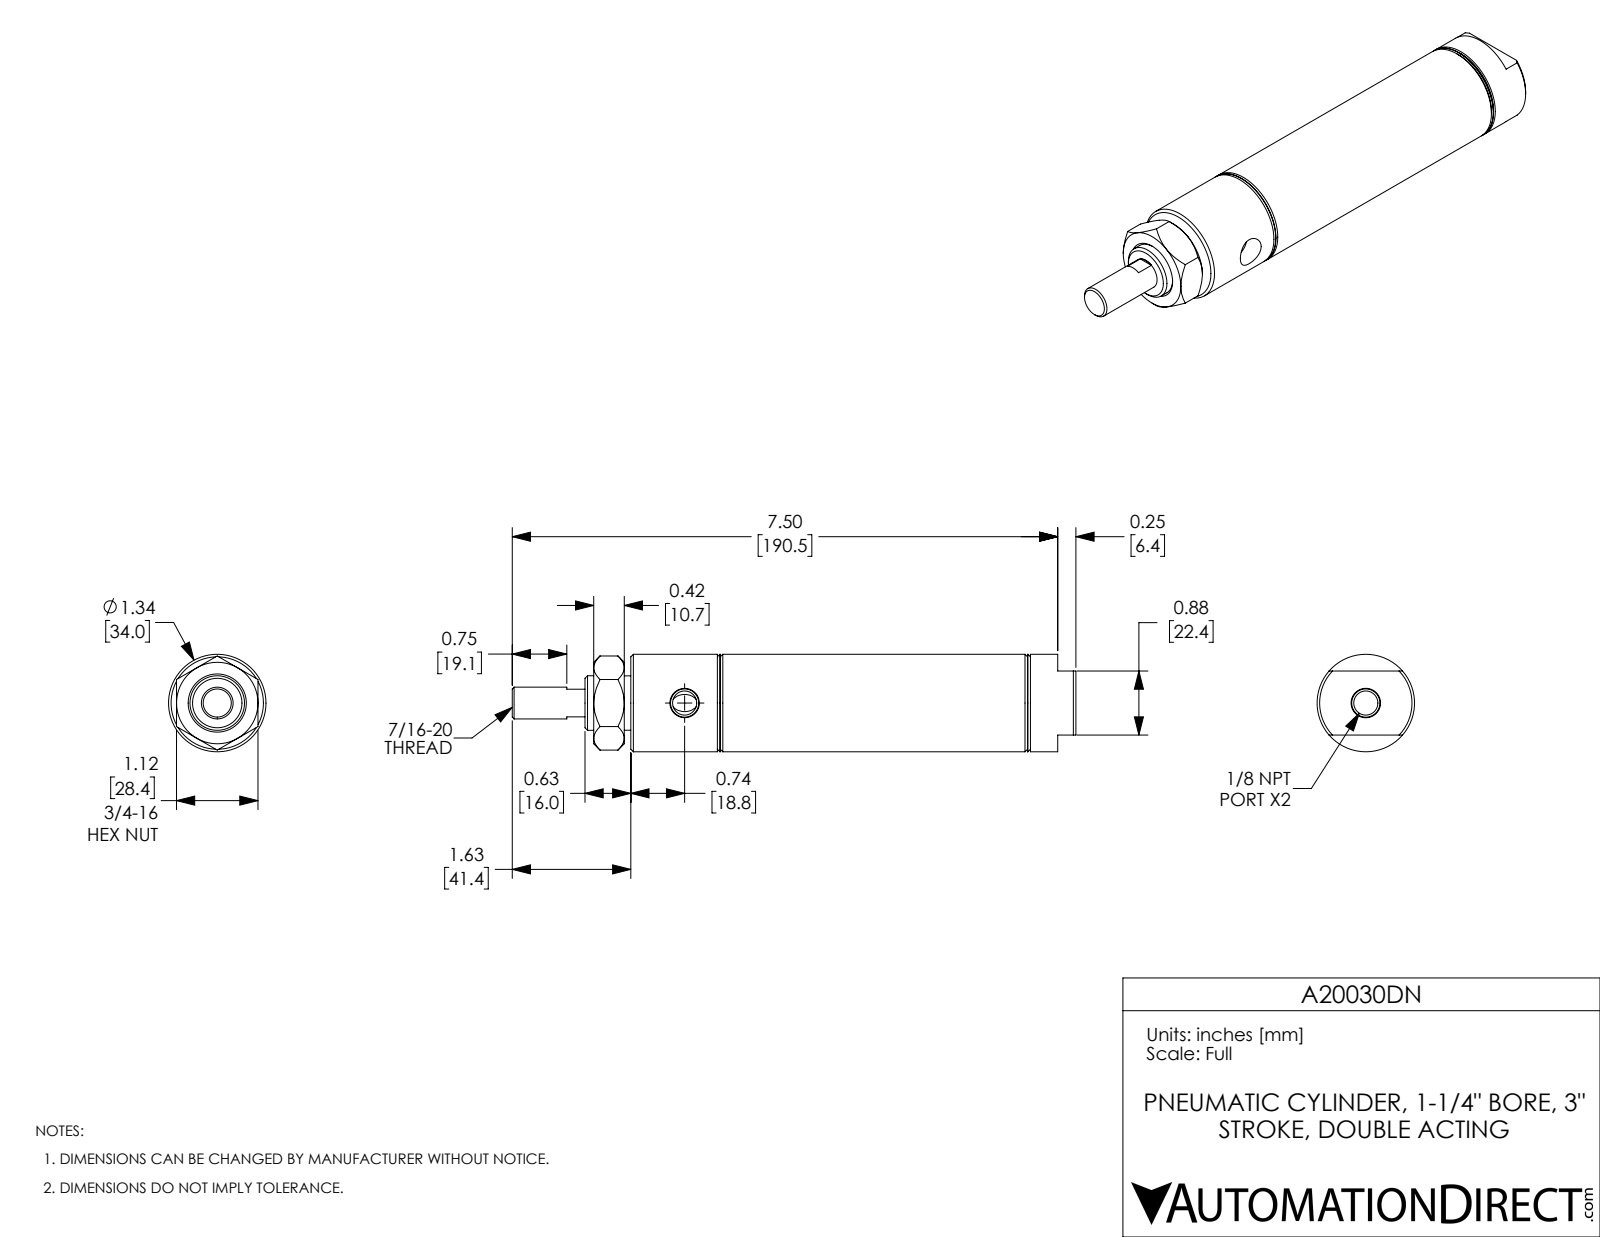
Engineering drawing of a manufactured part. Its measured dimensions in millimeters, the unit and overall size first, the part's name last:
Units: millimetres
Overall size (bounding box): 196.9 × 34 × 34
Round holes (diameter × count): ⌀8.4 ×2, ⌀11.1 ×1, ⌀19.1 ×1, ⌀31.8 ×1
Round bosses / shafts (diameter × count): ⌀34 ×1, ⌀19 ×1
Main face-to-face distances: 88.9, 12.7, 76.2, 33.3, 46, 122.2, 155.4, 122.2, 109.5, 33.3
Volume: 95 370 mm³ · Surface area: 43 260 mm²
Bodies: 3 solids, 100 faces (33 planar, 28 cylindrical, 39 other)
Part name (STEP PRODUCT): A20030DN-MainBody; A20030DN-Rod; A20030DN_Mounting Nut_D-3556; A20030DN
STEP written by: SolidWorks 2017 (AUTOMOTIVE_DESIGN)
